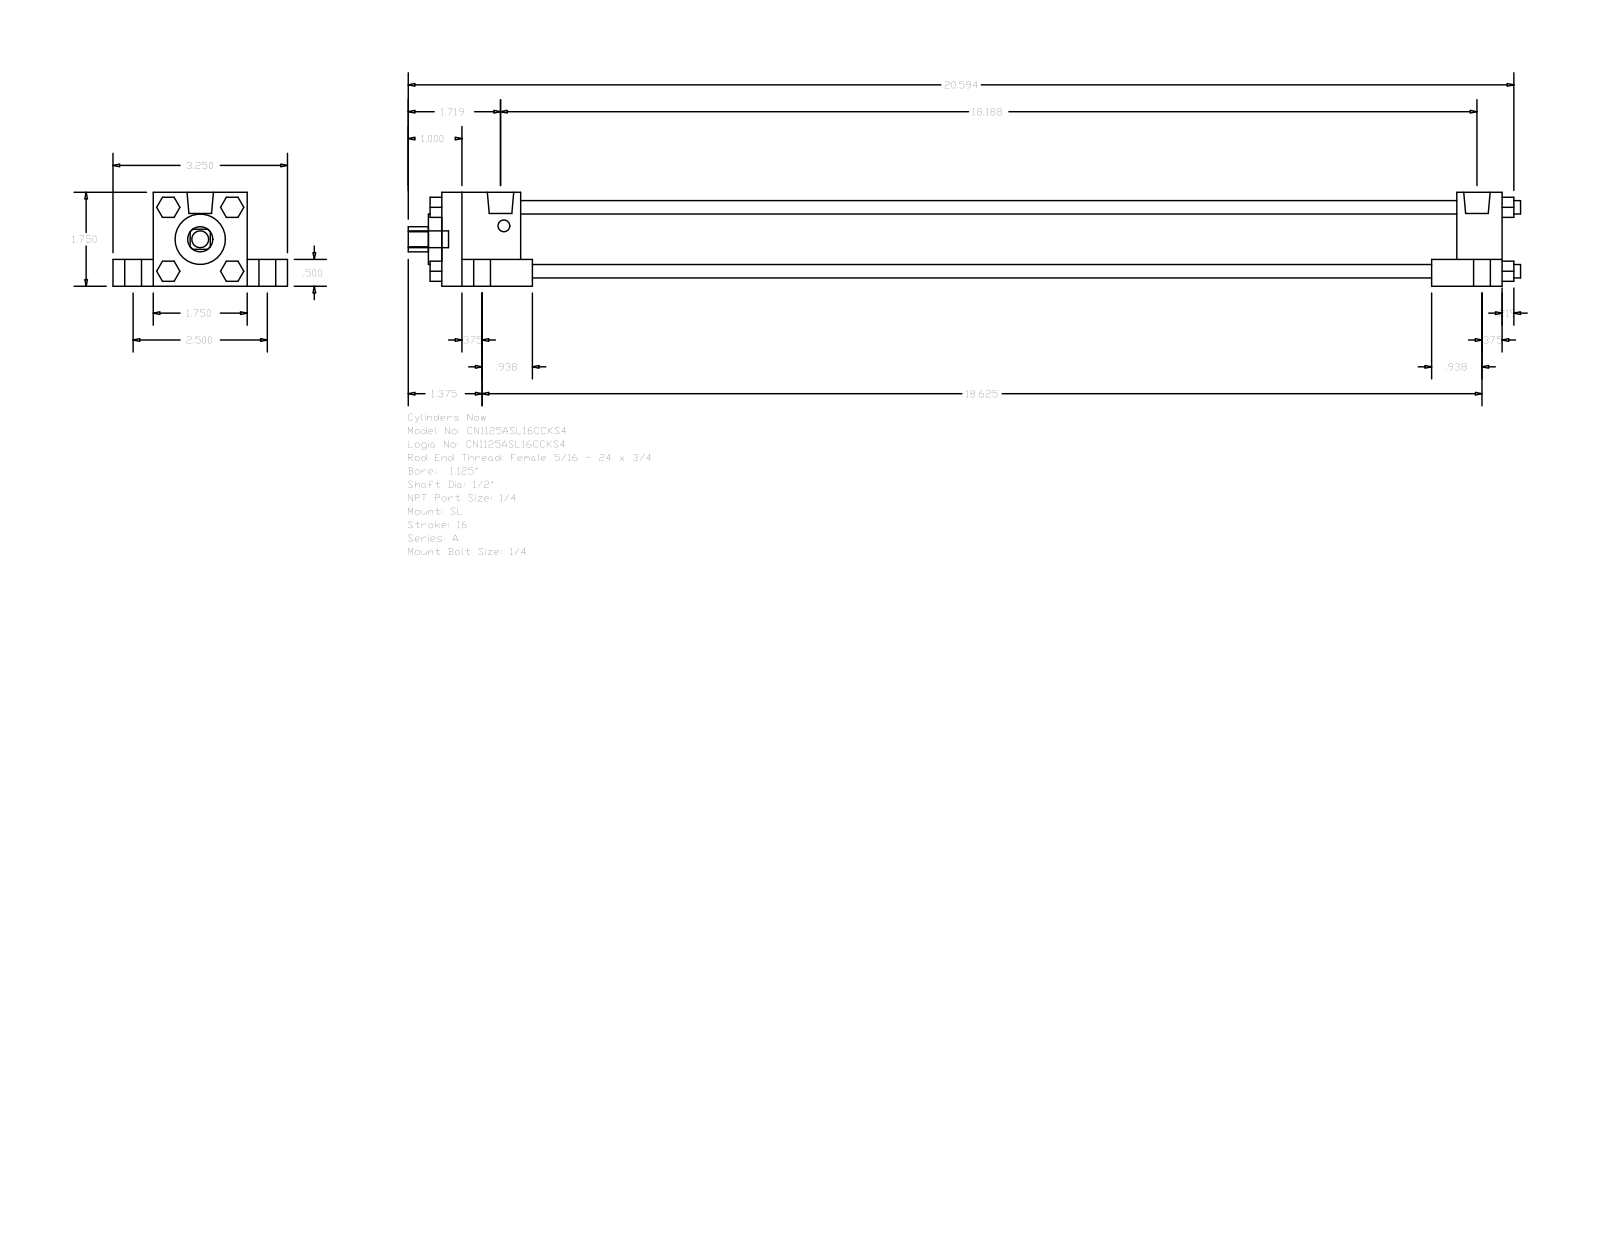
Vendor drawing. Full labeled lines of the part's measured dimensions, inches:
Part name (STEP PRODUCT): A_SL__0112_0.5
STEP written by: GSSL Pune (CONFIG_CONTROL_DESIGN)
Units: inches
Bodies: 0 solids, 150 faces (114 planar, 36 cylindrical, 0 other)
Overall size (bounding box): 20.719 × 3.25 × 1.75
Round holes (diameter × count): ⌀0.5 ×1, ⌀0.937 ×1, ⌀1.255 ×1
Round bosses / shafts (diameter × count): ⌀0.313 ×5, ⌀0.563 ×4, ⌀0.25 ×4, ⌀0.219 ×4, ⌀0.492 ×2
Partial cylindrical surfaces — rounded edges, fillets, slot ends (radius × count): R0.234 ×1
Main face-to-face distances: 1.75, 1.25, 0.5, 0.75, 2.5, 18.281, 19.75, 18.906, 0.844, 1.469
